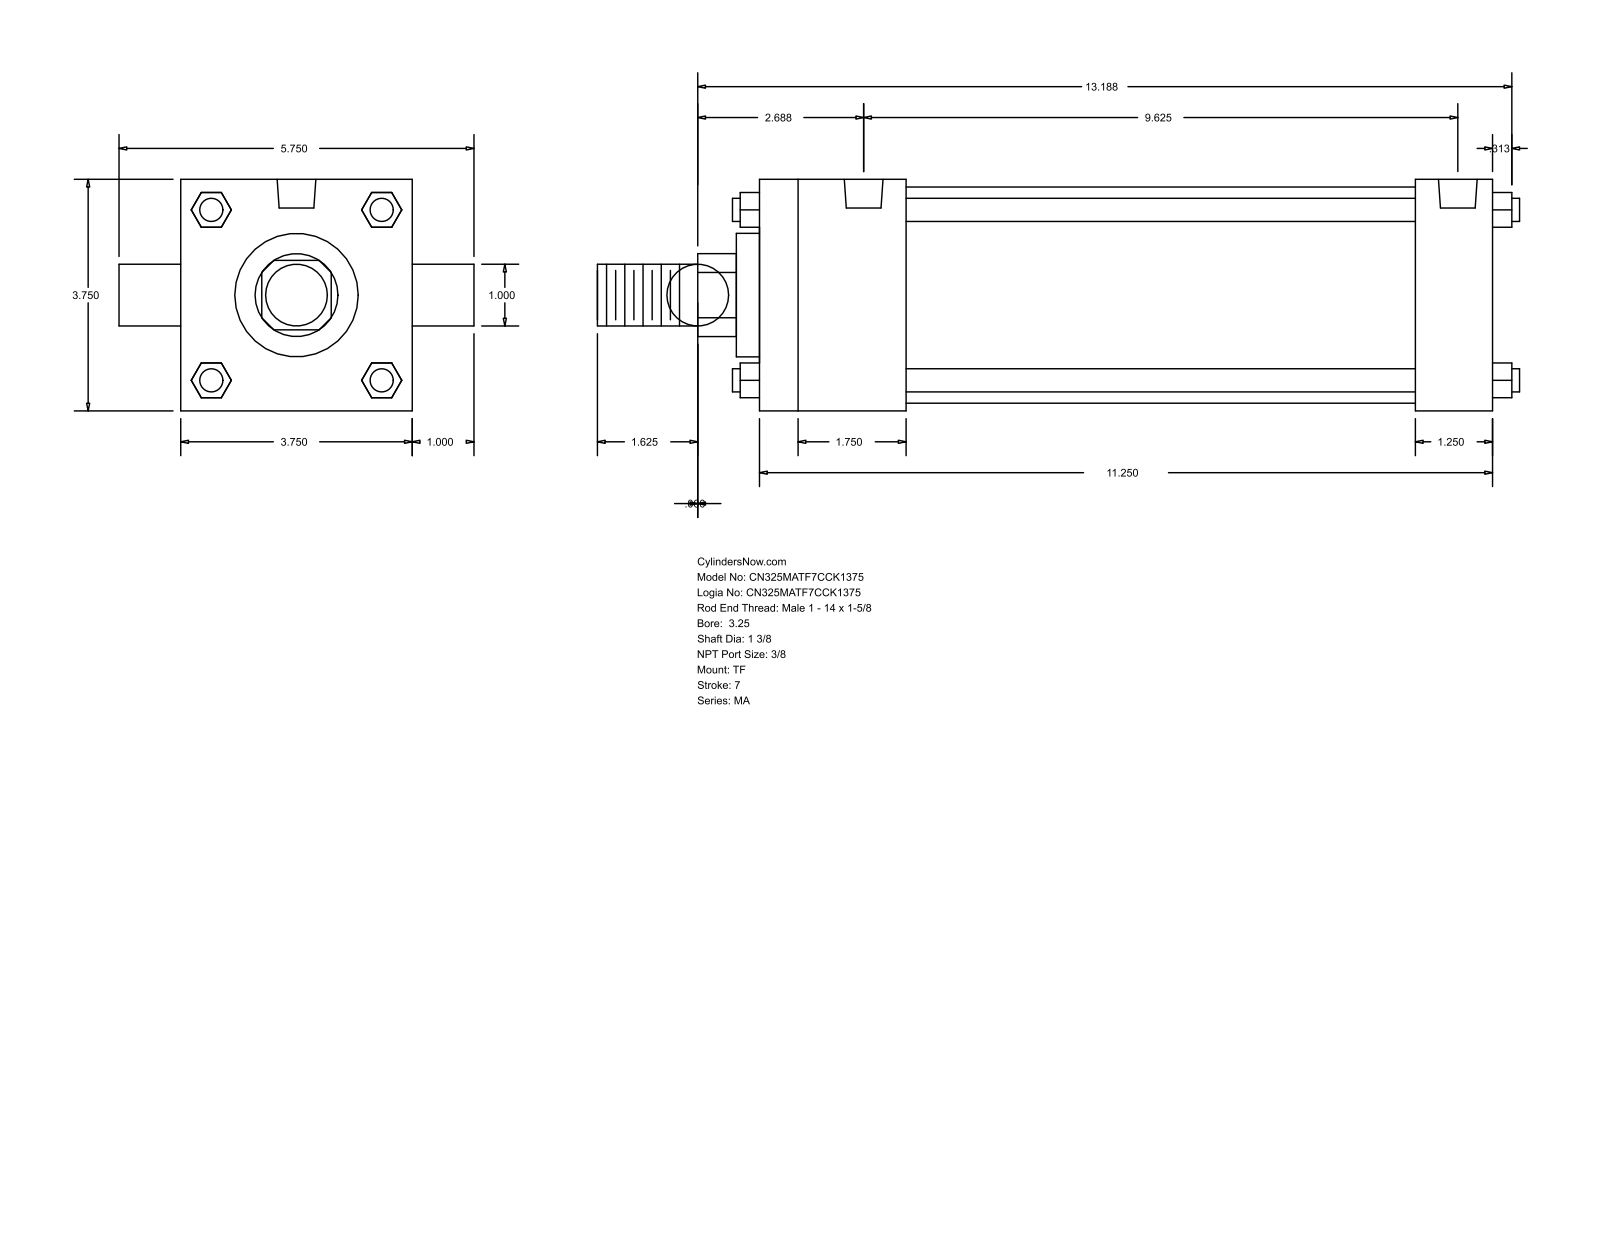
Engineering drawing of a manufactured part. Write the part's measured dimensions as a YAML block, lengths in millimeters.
part_name: "MA_TF__0325_1.375"
step_written_by: "GSSL Pune (CONFIG_CONTROL_DESIGN)"
units: millimeters
bodies: {solids: 0, faces: 120, planar: 92, cylindrical: 28, other: 0}
overall_size: [379.41, 146.05, 95.25]
round_holes:
  - {diameter: 11.11, count: 3}
  - {diameter: 15.93, count: 2}
round_bosses_or_shafts:
  - {diameter: 9.53, count: 4}
  - {diameter: 25.4, count: 2}
  - {diameter: 88.9, count: 1}
  - {diameter: 50.8, count: 1}
  - {diameter: 34.92, count: 1}
partial_cylinders:
  - {radius: 17.06, count: 1}
face_to_face_distances: [95.24, 301.62, 60.32, 269.87, 209.55, 241.3, 31.75, 9.52, 69.84, 279.39]
hole_center_spacings: [4.76, 4.77, 234.95, 239.71, 239.72, 244.48]
